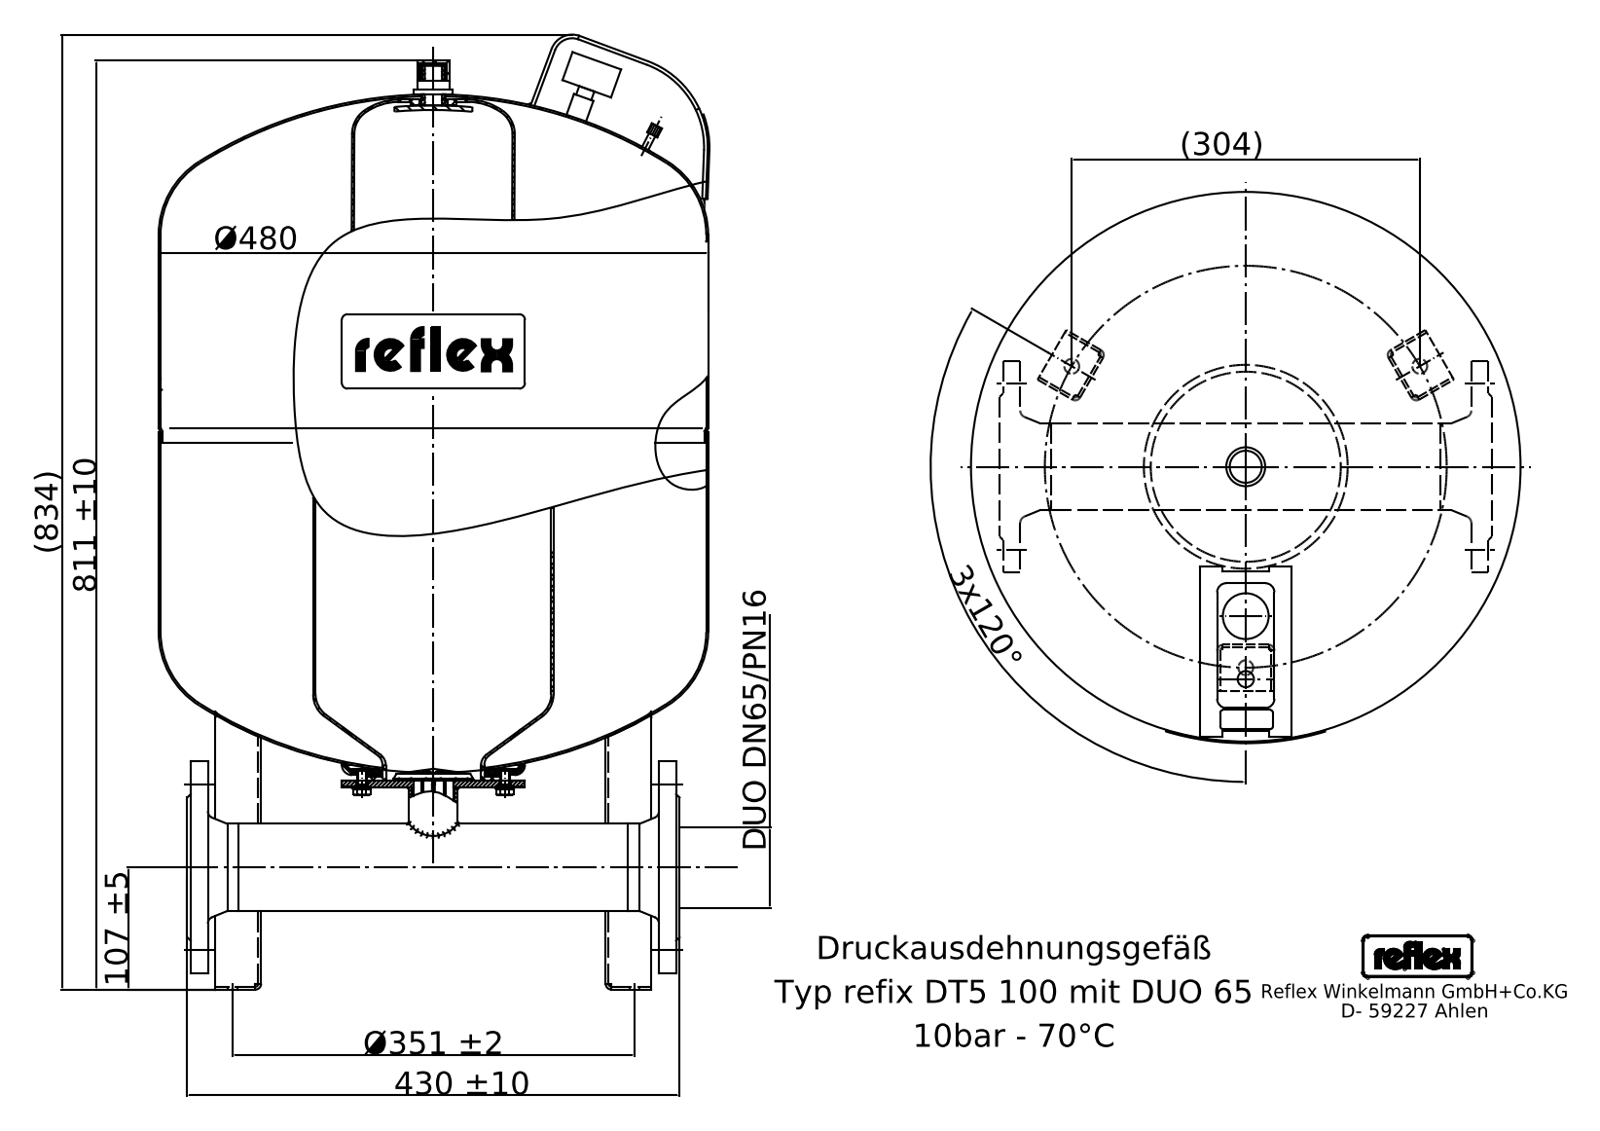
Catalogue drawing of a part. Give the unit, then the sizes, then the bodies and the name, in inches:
Units: inches
Overall size (bounding box): 32.608 × 18.898 × 18.898
Round holes (diameter × count): ⌀0.748 ×4, ⌀0.528 ×3, ⌀0.098 ×1, ⌀0.15 ×1, ⌀0.169 ×1, ⌀0.173 ×1, ⌀0.215 ×1, ⌀0.276 ×1, ⌀0.315 ×1, ⌀0.449 ×1, ⌀2.996 ×1, ⌀3.622 ×1
Round bosses / shafts (diameter × count): ⌀0.394 ×9, ⌀18.898 ×1, ⌀7.283 ×1, ⌀6.299 ×1, ⌀5.512 ×1, ⌀2.441 ×1, ⌀1.669 ×1, ⌀1.339 ×1
Partial cylindrical surfaces — rounded edges, fillets, slot ends (radius × count): R0.039 ×15, R0.098 ×15, R0.197 ×15, R0.155 ×4, R0.062 ×3, R0.106 ×2, R0.186 ×2, R0.256 ×2
Main face-to-face distances: 12.717, 0.098, 1.87, 1.969, 1.772, 5.551, 18.268, 0.236, 5.787, 18.504
Hole centre spacings: 2.855, 4.037, 6.909, 11.968, 5.709
Volume: 5 725 in³ · Surface area: 3 638 in²
Bodies: 23 solids, 533 faces (226 planar, 189 cylindrical, 118 other)
STEP written by: Mechanical Desktop 2008 (CONFIG_CONTROL_DESIGN)
